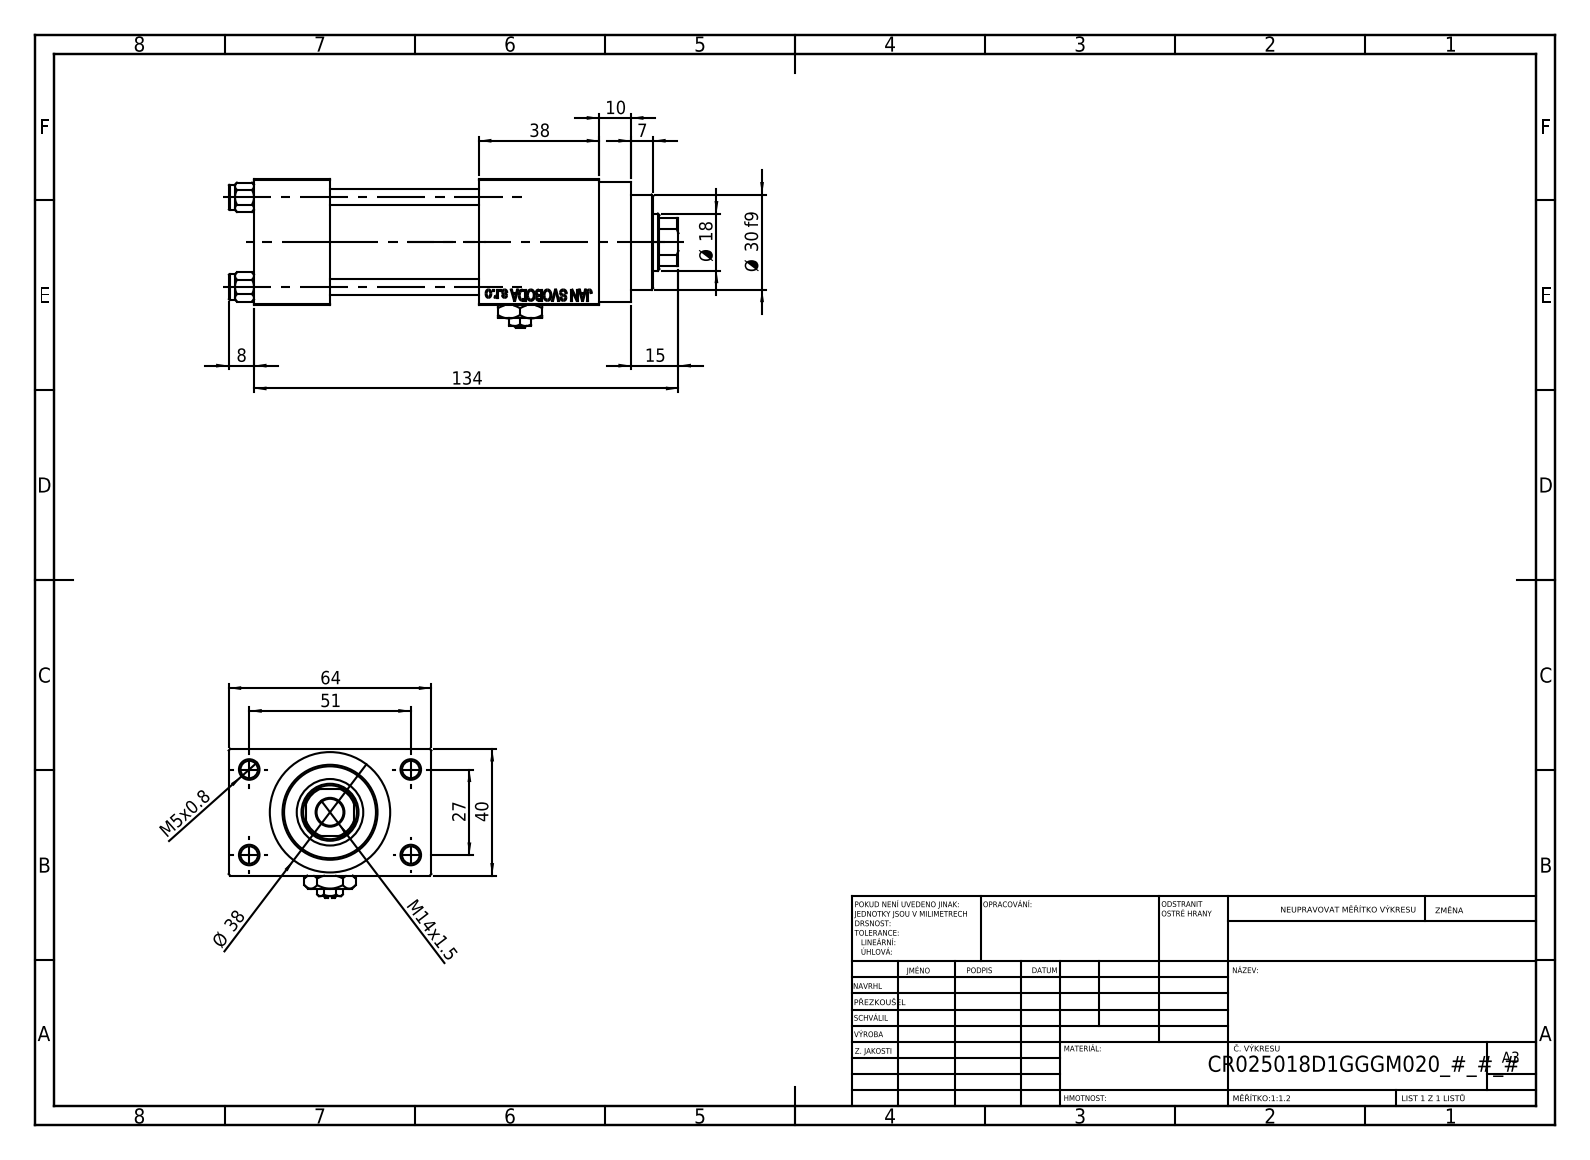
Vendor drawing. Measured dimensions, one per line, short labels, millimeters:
name: V215CR_VCP_D; V215CR_D_Body; V215_VC_A; NUT_M5_D (+2 more)
written by: SolidWorks 2019 (CONFIG_CONTROL_DESIGN)
unit: mm
bodies: 12 solids, 1147 faces (518 planar, 91 cylindrical, 538 other)
size: 142 × 64 × 47
volume: 180 837 mm³; area: 64 776 mm²
holes: 4× ⌀5, 4× ⌀5.5, 3× ⌀20, 2× ⌀7, 2× ⌀13.16, 1× ⌀8.5, 1× ⌀18, 1× ⌀21, 1× ⌀25, 1× ⌀30
bosses: 4× ⌀8, 1× ⌀38, 1× ⌀31
rounds: 1× R8.5
face distances: 40, 12, 52, 47, 24, 71, 64, 38, 85, 109
hole spacings: 11.37, 20.01, 28.3, 28.85, 29.89, 39.66, 48.34, 27
